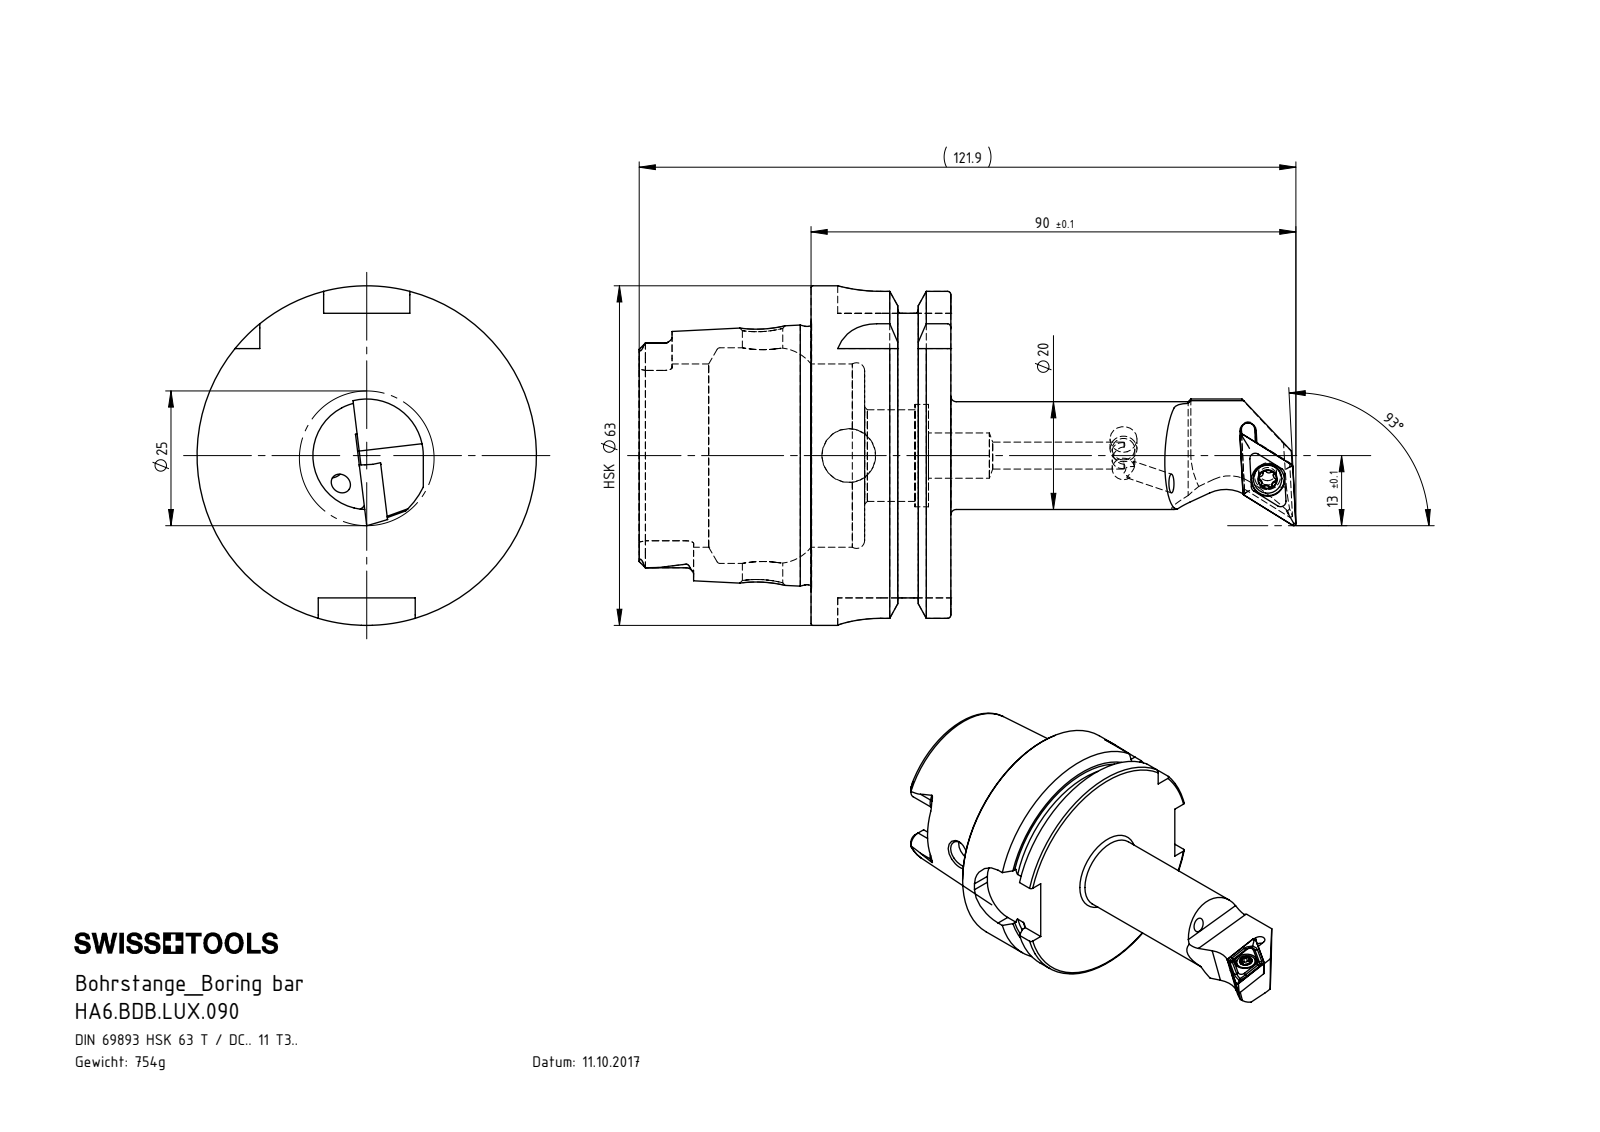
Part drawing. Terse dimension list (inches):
name: HA6.BDB.LUX.090; KVT_MB_600_050; WCB-ER2.001.009_A; DCMT11T304 (+1 more)
written by: SolidWorks 2017 (AUTOMOTIVE_DESIGN)
unit: in
bodies: 5 solids, 313 faces (80 planar, 92 cylindrical, 141 other)
size: 4.799 × 2.48 × 2.48
volume: 5.849 in³; area: 43.16 in²
holes: 2× ⌀0.13, 1× ⌀0.157, 1× ⌀0.165, 1× ⌀0.173, 1× ⌀0.197, 1× ⌀0.24, 1× ⌀0.295, 1× ⌀0.331, 1× ⌀0.394, 1× ⌀0.669, 1× ⌀0.748, 1× ⌀1.339
bosses: 1× ⌀2.48, 1× ⌀2.163, 1× ⌀1.887, 1× ⌀0.787, 1× ⌀0.207, 1× ⌀0.197, 1× ⌀0.157
rounds: 6× R0.013, 6× R0.023, 6× R0.055, 4× R0.315, 2× R0.111, 2× R0.113, 1× R0.049, 1× R0.118
face distances: 1.022, 0.63, 0.392, 1.256, 1.648, 2.278, 2.079, 0.858, 0.467, 2.114
